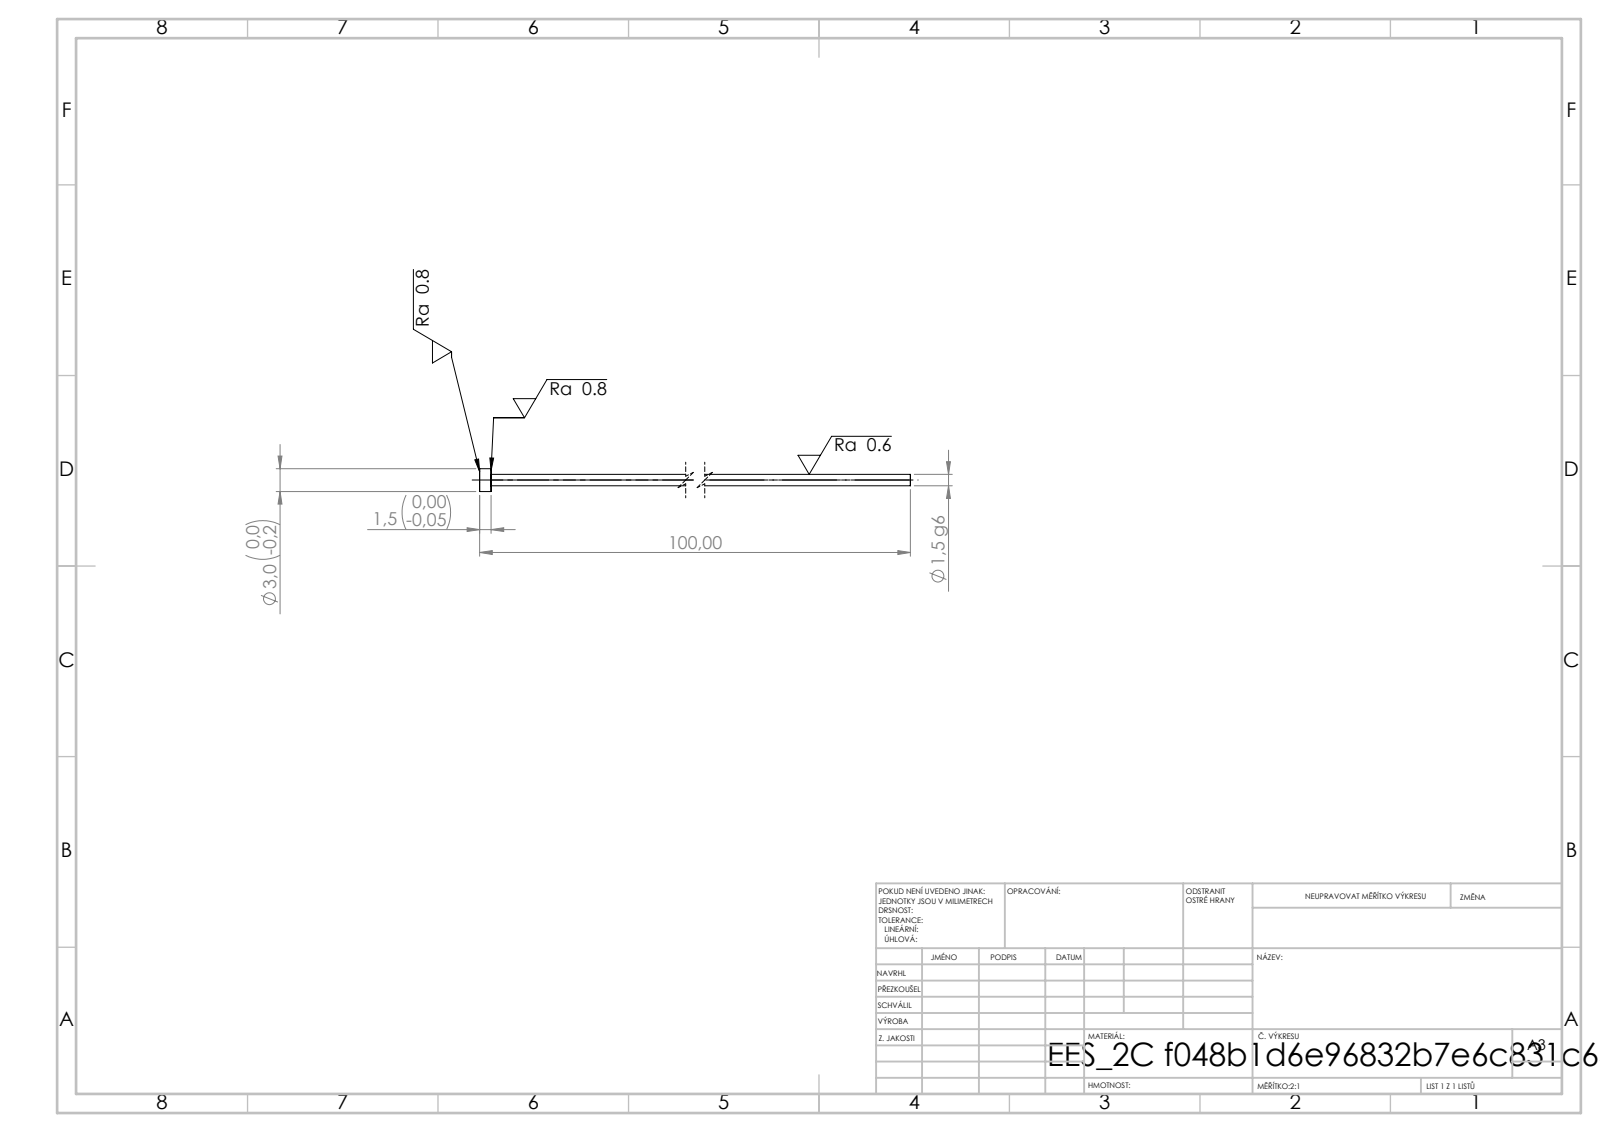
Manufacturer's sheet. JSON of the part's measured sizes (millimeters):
{"step_written_by": "SolidWorks 2019 (CONFIG_CONTROL_DESIGN)", "units": "millimeters", "bodies": {"solids": 1, "faces": 7, "planar": 3, "cylindrical": 4, "other": 0}, "overall_size": [100, 3, 3], "volume_mm3": 185, "surface_area_mm2": 492, "round_bosses_or_shafts": [[3, 1], [1.5, 1]], "face_to_face_distances": [1.5, 100, 98.5]}
